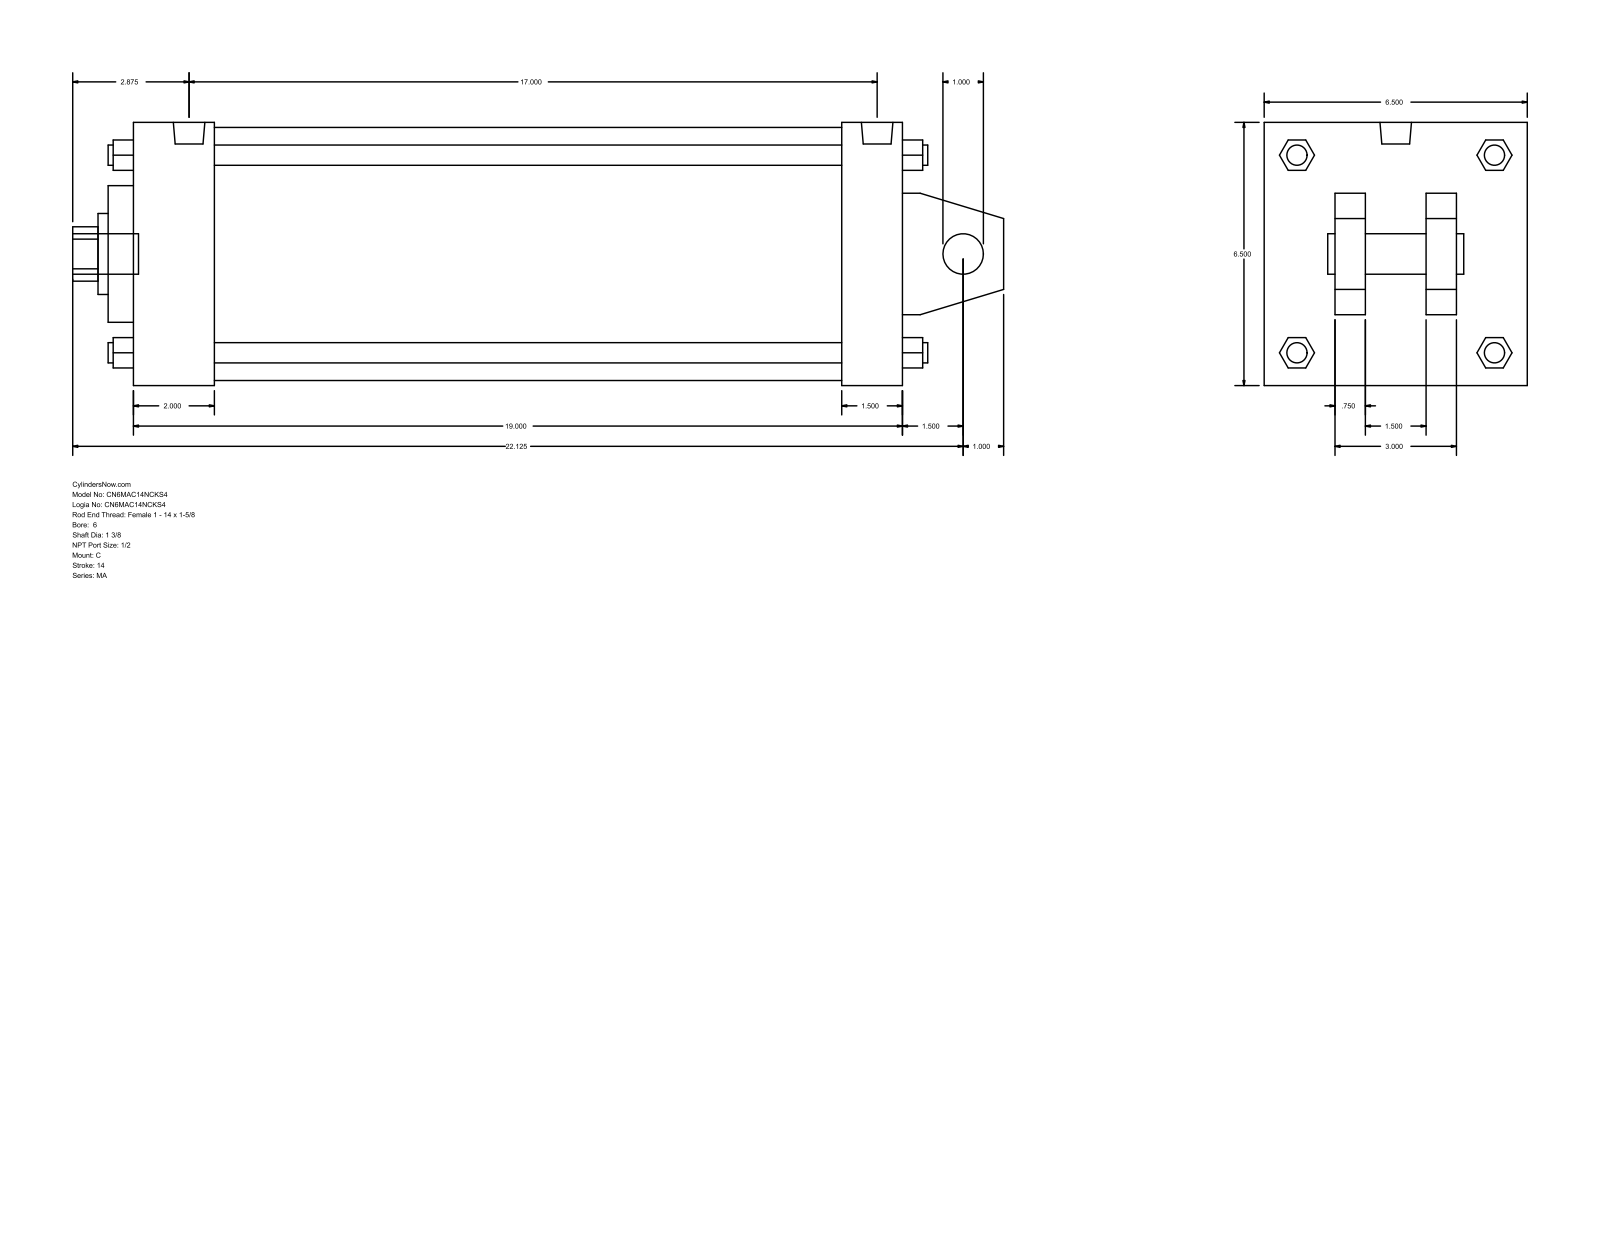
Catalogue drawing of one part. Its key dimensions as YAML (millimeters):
part_name: "MA_C__0600_1.375"
step_written_by: "GSSL Pune (CONFIG_CONTROL_DESIGN)"
units: millimeters
bodies: {solids: 0, faces: 141, planar: 109, cylindrical: 32, other: 0}
overall_size: [584.2, 165.1, 165.1]
round_holes:
  - {diameter: 25.4, count: 1}
  - {diameter: 34.92, count: 1}
  - {diameter: 50.8, count: 1}
  - {diameter: 85.72, count: 1}
  - {diameter: 158.75, count: 1}
round_bosses_or_shafts:
  - {diameter: 17.46, count: 4}
  - {diameter: 12.7, count: 4}
  - {diameter: 19.77, count: 2}
  - {diameter: 25.4, count: 1}
partial_cylinders:
  - {radius: 17.06, count: 1}
face_to_face_distances: [165.1, 482.6, 38.1, 19.05, 63.5, 101.6, 50.8, 44.45, 120.65, 444.5]
